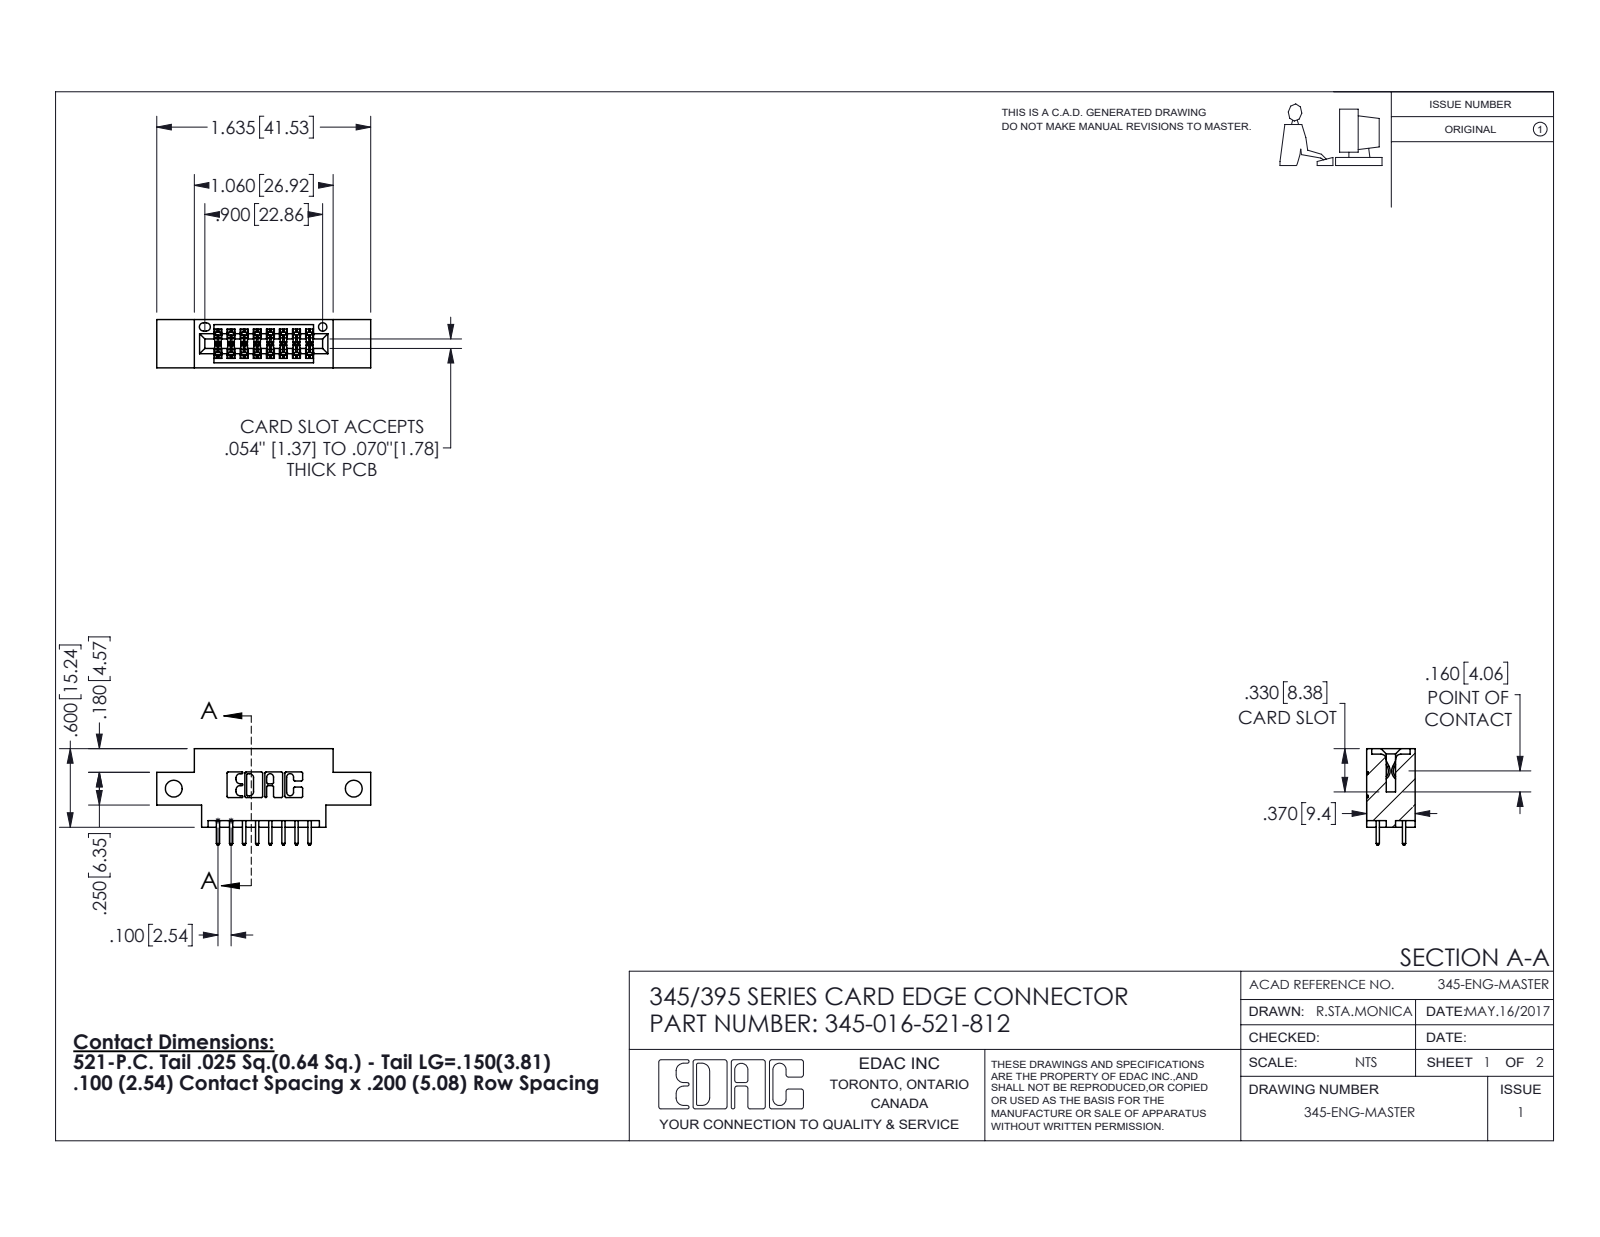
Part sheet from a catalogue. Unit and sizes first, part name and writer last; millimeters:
Units: millimetres
Overall size (bounding box): 41.5 × 18.7 × 9.4
Round holes (diameter × count): ⌀3.3 ×2, ⌀1.6 ×1
Partial cylindrical surfaces — rounded edges, fillets, slot ends (radius × count): R0.2 ×24, R0.3 ×22, R0.3 ×16, R0.2 ×6, R0.8 ×6, R0.7 ×3, R0.4 ×2, R0.5 ×2
Main face-to-face distances: 5.1, 9.4, 7.6, 1.8, 2.5, 2.5, 6.9, 0.6, 5.7, 1.5
Hole centre spacings: 34.9
Volume: 3 510 mm³ · Surface area: 4 497 mm²
Bodies: 17 solids, 930 faces (612 planar, 318 cylindrical, 0 other)
Part name (STEP PRODUCT): 345-292-001_345-293-121; 345-016-521-812; 345 Part_0.170 Offset - Side Mount
STEP written by: SolidWorks 2016 (CONFIG_CONTROL_DESIGN)
